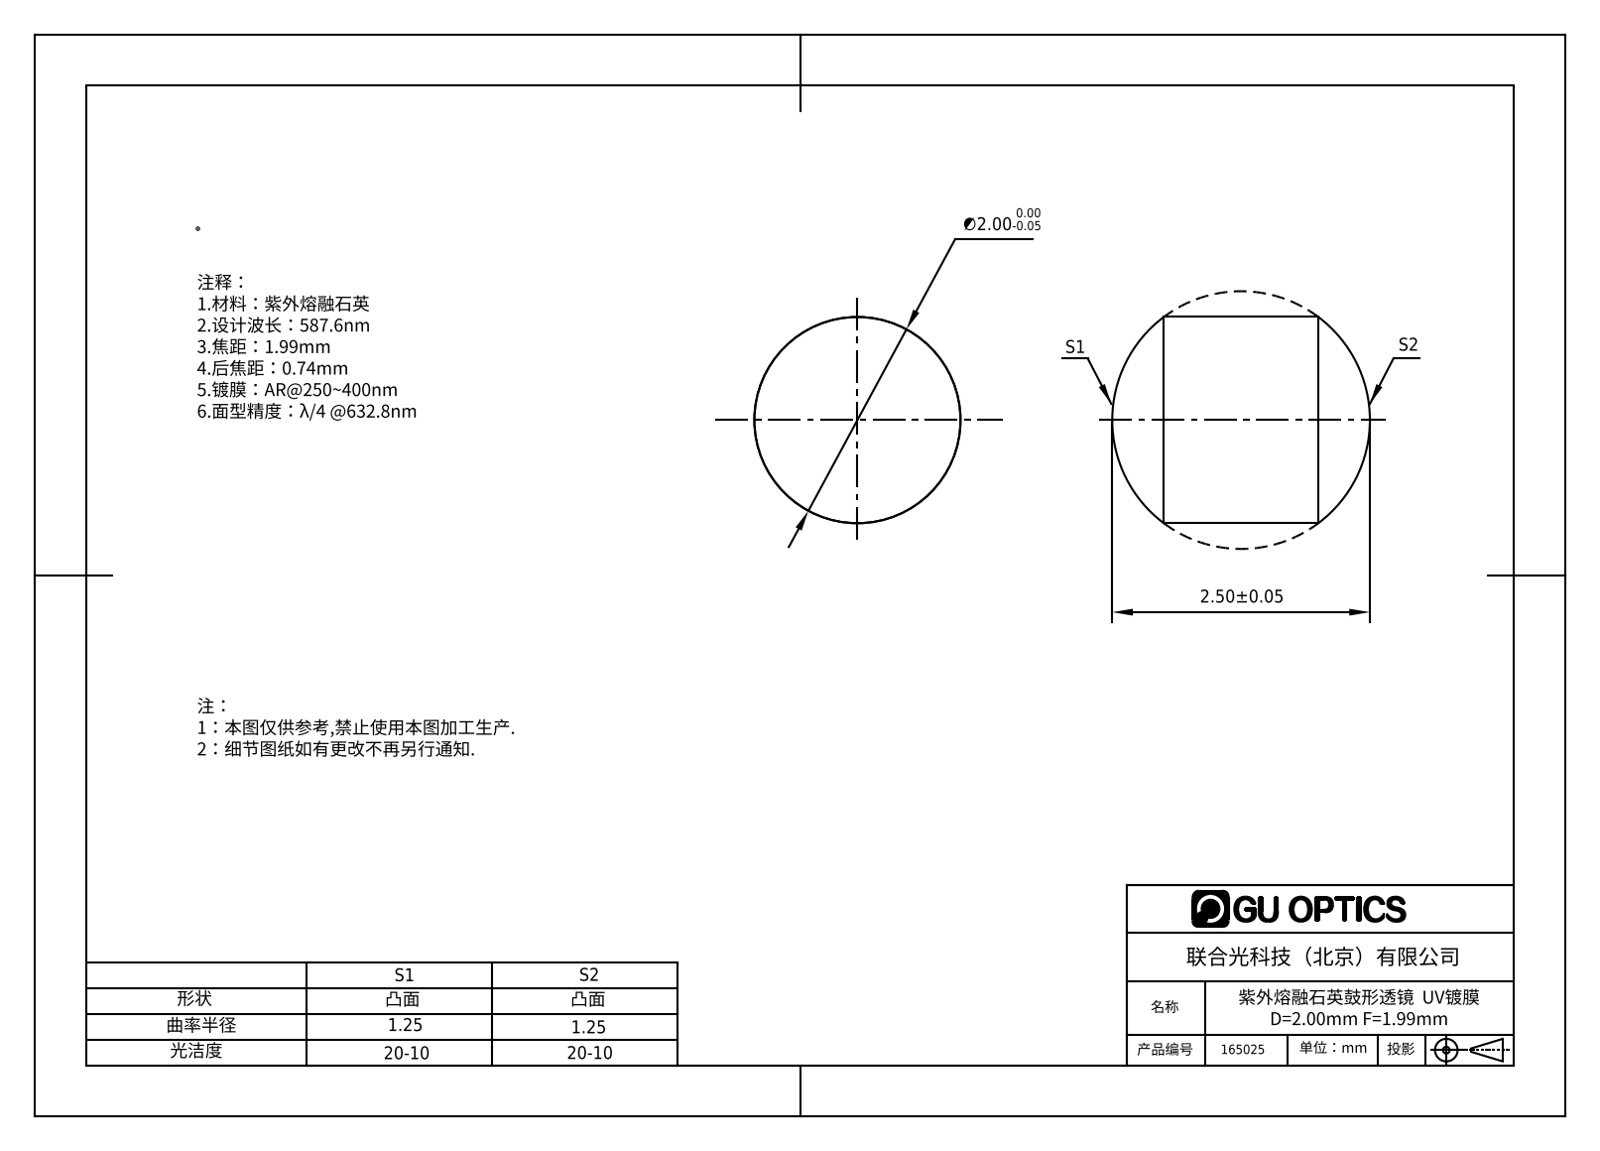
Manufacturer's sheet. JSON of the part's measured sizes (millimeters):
{"part_name": "165000鼓形", "step_written_by": "SolidWorks 2016 (CONFIG_CONTROL_DESIGN)", "units": "millimeters", "bodies": {"solids": 1, "faces": 6, "planar": 0, "cylindrical": 2, "other": 4}, "overall_size": [2.5, 2, 2], "volume_mm3": 6, "surface_area_mm2": 17, "round_bosses_or_shafts": [[2, 1]]}
